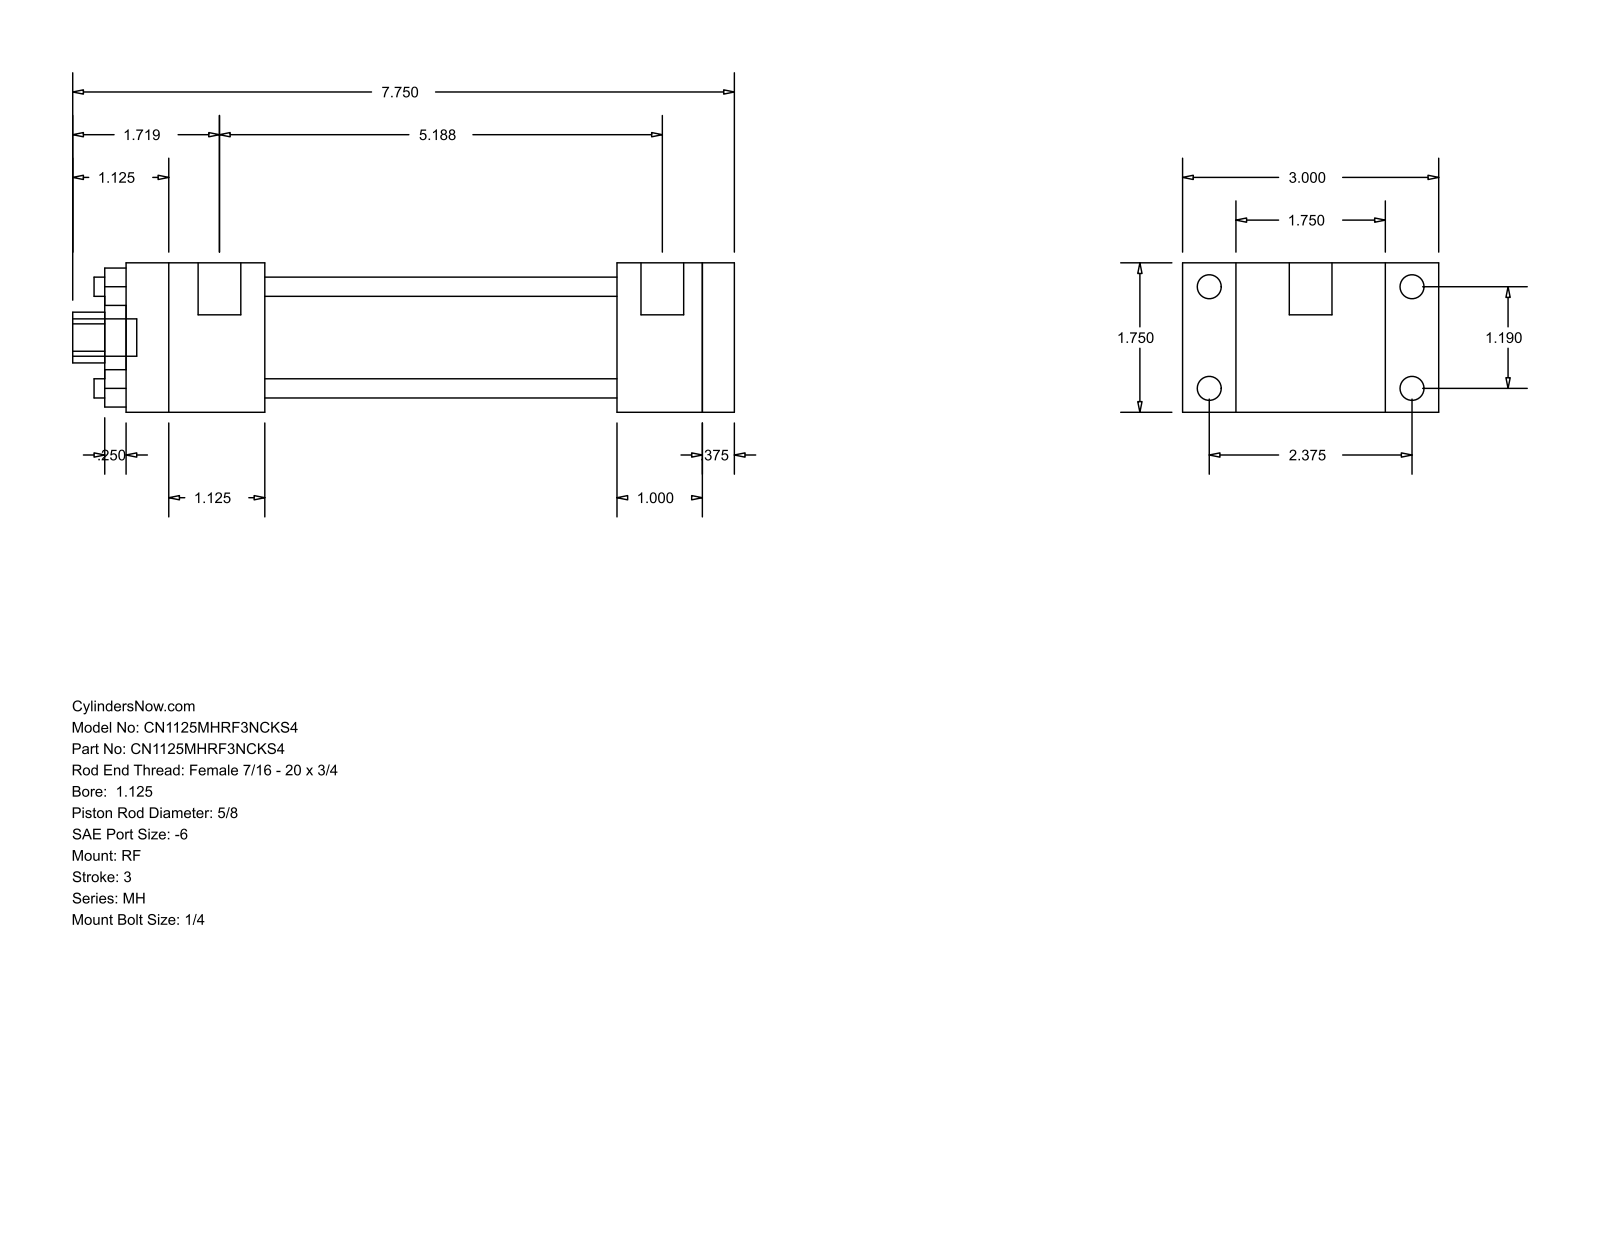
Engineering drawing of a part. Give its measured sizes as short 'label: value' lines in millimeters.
name: MH_RF__0112_0.625
written by: GSSL Pune (CONFIG_CONTROL_DESIGN)
unit: mm
bodies: 0 solids, 92 faces (64 planar, 28 cylindrical, 0 other)
size: 196.85 × 76.2 × 44.45
holes: 4× ⌀5.71, 1× ⌀15.88, 1× ⌀28.57, 1× ⌀34.92
bosses: 4× ⌀7.14, 4× ⌀5.56, 2× ⌀12.7, 1× ⌀11.11
rounds: 1× R7.54
face distances: 44.46, 9.53, 180.97, 15.87, 130.17, 139.7, 104.78, 25.39, 34.92, 41.27
hole spacings: 21.37, 30.22, 42.74
